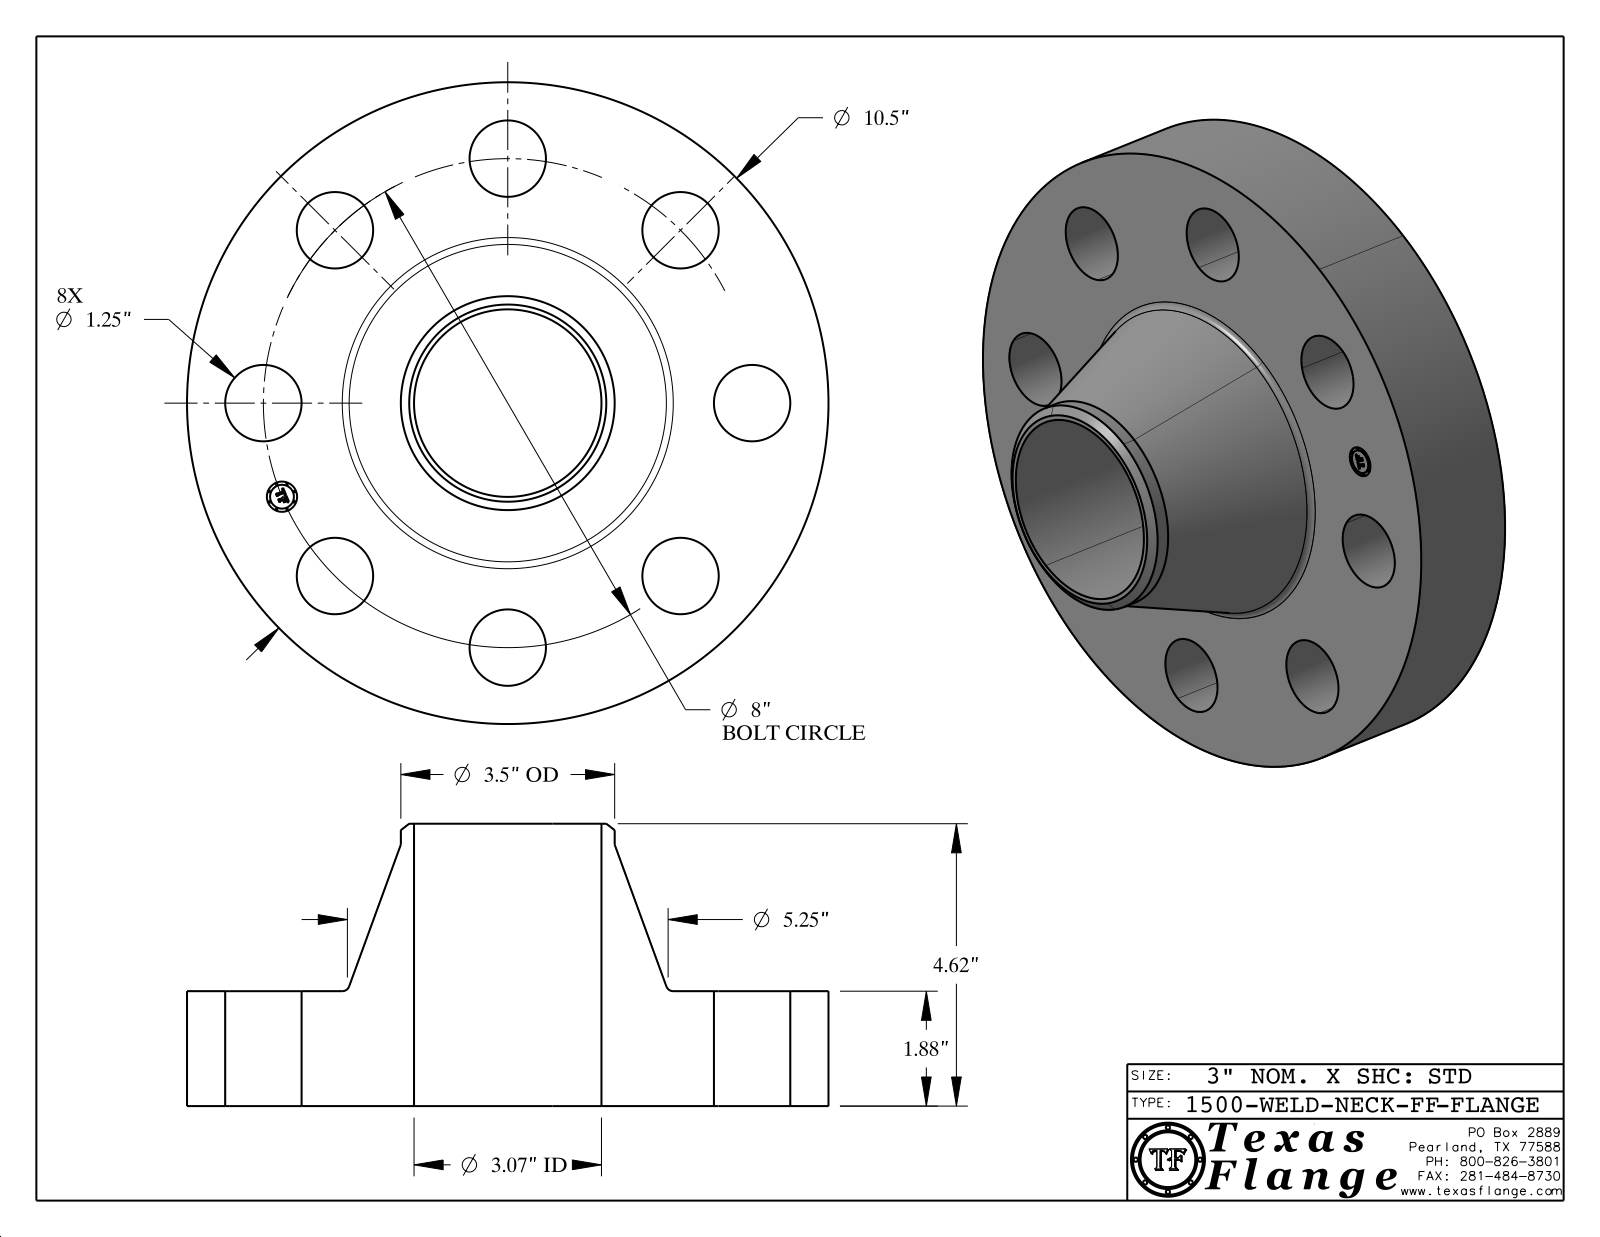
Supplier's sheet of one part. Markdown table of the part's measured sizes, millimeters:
| quantity | value |
| --- | --- |
| part name | 1500-WELD-NECK-FF |
| STEP written by | CATIA V5 STEP AP214 (AUTOMOTIVE_DESIGN) |
| units | millimeters |
| bodies | 1 solid, 416 faces (368 planar, 42 cylindrical, 6 other) |
| overall size | 266.7 × 266.7 × 117.3 |
| volume | 2 456 000 mm³ |
| surface area | 213 000 mm² |
| round holes (diameter × count) | 31.8 × 8, 12.6 × 1, 77.9 × 1 |
| round bosses / shafts (diameter × count) | 0.8 × 8, 266.7 × 1, 88.9 × 1, 9.9 × 1 |
| main face-to-face distances | 47.8, 117.3, 69.6, 0.4, 47.4, 70, 3.8, 3.7, 0.7, 2.4 |
| hole center spacings | 101.6, 77.7, 143.7, 187.7, 39.6, 169, 199.3, 203.2 |
